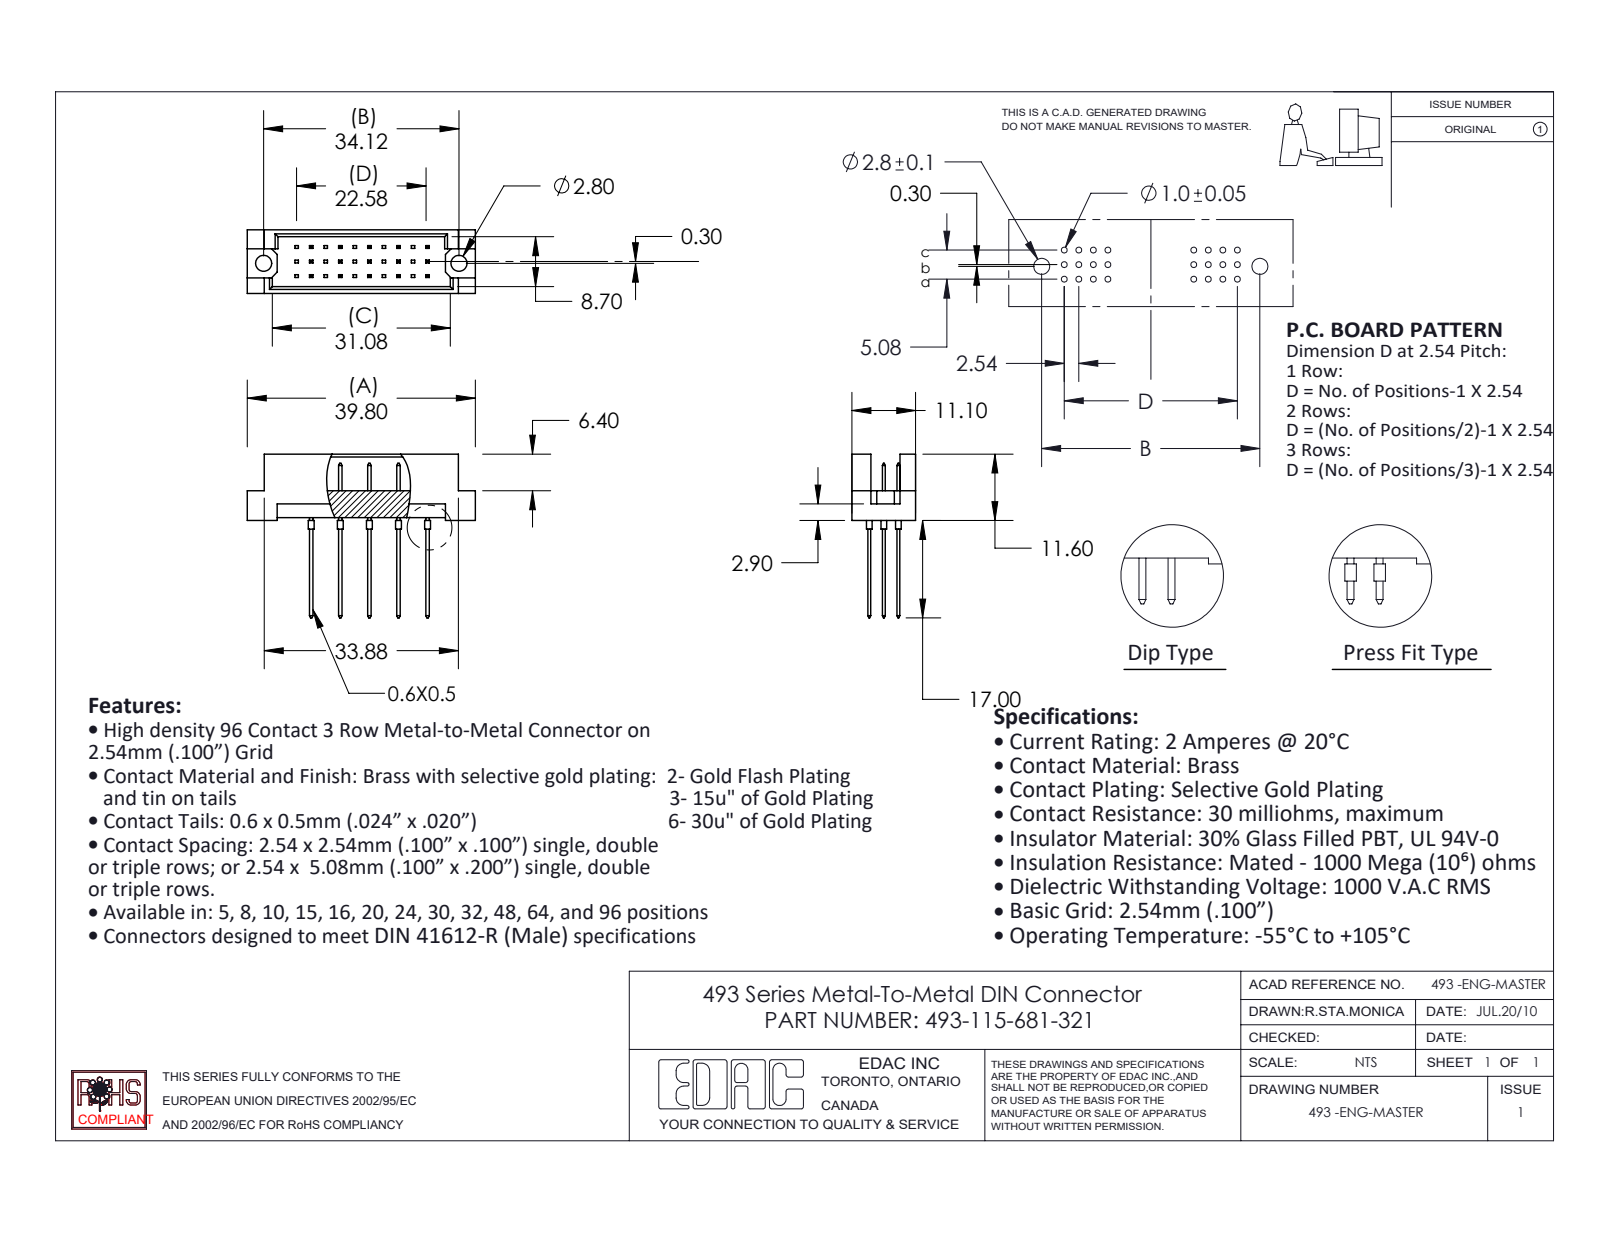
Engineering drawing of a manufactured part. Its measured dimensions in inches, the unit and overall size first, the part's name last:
Units: inches
Overall size (bounding box): 1.567 × 1.126 × 0.437
Round holes (diameter × count): ⌀0.11 ×2
Round bosses / shafts (diameter × count): ⌀0.039 ×15
Main face-to-face distances: 0.2, 0.047, 0.39, 0.02, 0.1, 0.437, 0.343, 0.4, 0.185, 0.024
Hole centre spacings: 1.343
Volume: 0.153 in³ · Surface area: 5.671 in²
Bodies: 16 solids, 502 faces (468 planar, 34 cylindrical, 0 other)
Part name (STEP PRODUCT): 493-115-681-321; 493 Part_30; 493-290_81
STEP written by: SolidWorks 2020 (CONFIG_CONTROL_DESIGN)
